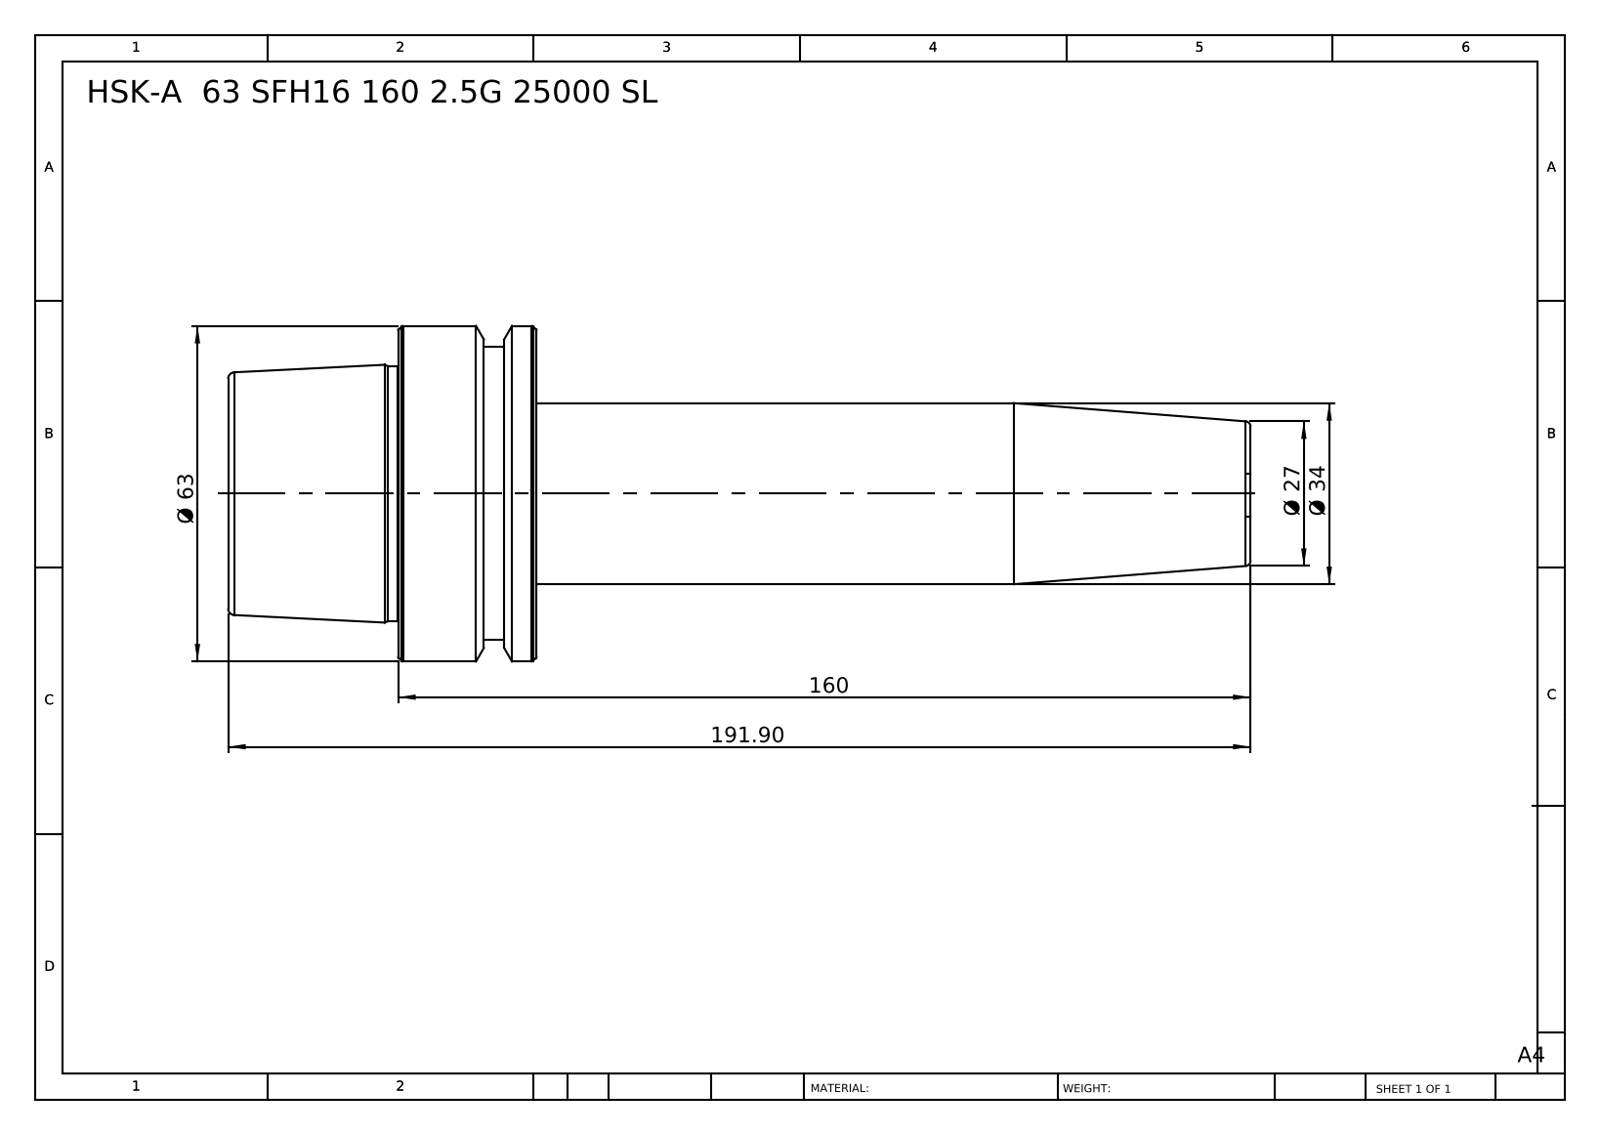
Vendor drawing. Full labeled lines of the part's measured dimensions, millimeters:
Part name (STEP PRODUCT): HSK-A 63 SFH16 160 2.5G 25000 SL
STEP written by: SolidWorks 2014 (CONFIG_CONTROL_DESIGN)
Units: millimetres
Bodies: 1 solid, 46 faces (6 planar, 10 cylindrical, 30 other)
Overall size (bounding box): 191.9 × 63 × 63
Volume: 246 500 mm³ · Surface area: 30 120 mm²
Round bosses / shafts (diameter × count): ⌀63 ×1, ⌀55 ×1, ⌀47.78 ×1, ⌀34 ×1
Main face-to-face distances: 57.9, 26, 31.9, 134, 160, 191.9, 140.1, 6.1, 19.9, 51.8
